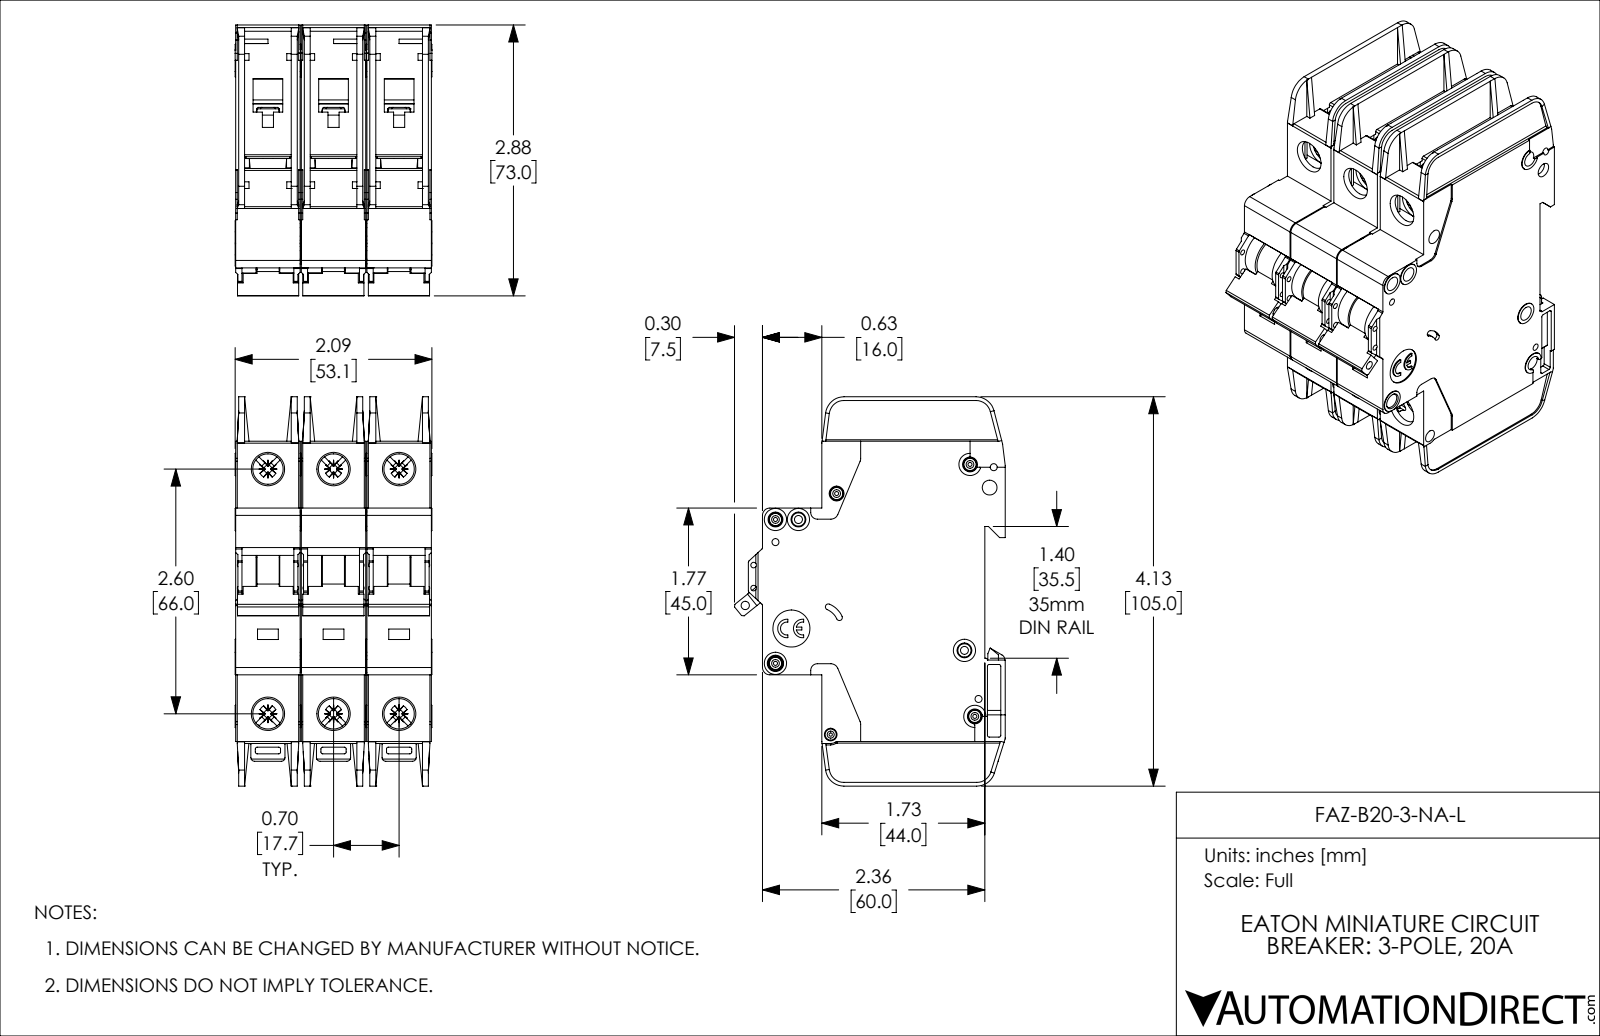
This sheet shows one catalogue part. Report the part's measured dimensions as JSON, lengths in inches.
{"part_name": "FAZ-B20-3-NA-L", "step_written_by": "SolidWorks 2019 (AUTOMOTIVE_DESIGN)", "units": "inches", "bodies": {"solids": 3, "faces": 3381, "planar": 2013, "cylindrical": 1071, "other": 297}, "overall_size": [4.134, 2.876, 2.091], "volume_in3": 14.05, "surface_area_in2": 123, "round_holes": [[0.157, 8], [0.323, 6], [0.043, 5], [0.075, 4], [0.059, 2], [0.085, 2], [0.035, 1], [0.089, 1], [0.098, 1], [0.134, 1], [0.394, 1]], "round_bosses_or_shafts": [[0.13, 5], [0.236, 4], [0.118, 4], [0.098, 3]], "partial_cylinders_radius": [[0.02, 72], [0.016, 30], [0.039, 18], [0.043, 12], [0.079, 12], [0.008, 6], [0.01, 6], [0.028, 6]], "face_to_face_distances": [0.697, 0.047, 1.394, 0.685, 0.591, 1.382, 0.744, 0.65, 0.106, 0.094], "hole_center_spacings": [0.697, 2.69, 2.598, 0.244, 0.537, 0.87, 1.394, 2.948]}
